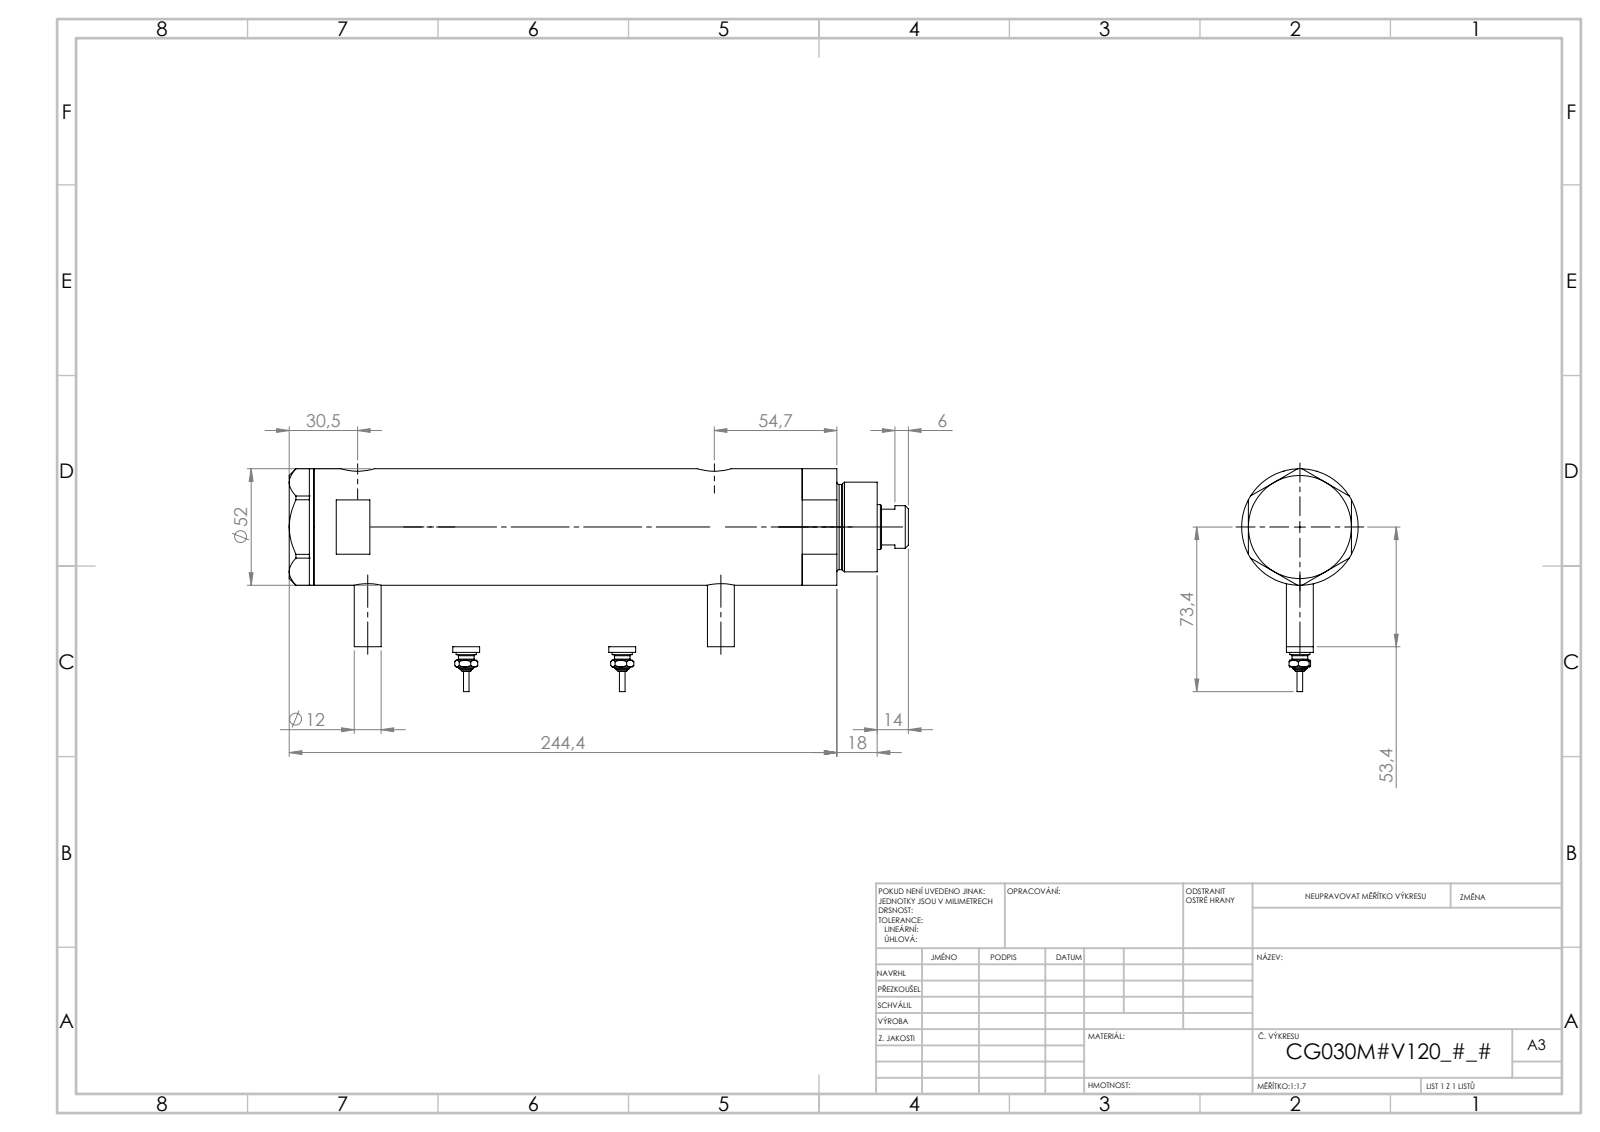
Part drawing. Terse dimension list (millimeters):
name: V270CG_VC; V270CG_BACK; V270CG_MIDDLE; V270CG_SWITCH (+1 more)
written by: SolidWorks 2019 (CONFIG_CONTROL_DESIGN)
unit: mm
bodies: 6 solids, 246 faces (95 planar, 77 cylindrical, 74 other)
size: 269.02 × 84.3 × 52
volume: 478 097 mm³; area: 105 489 mm²
holes: 2× ⌀5, 2× ⌀9.73, 2× ⌀12.5, 2× ⌀15, 1× ⌀6.5, 1× ⌀20, 1× ⌀21.5, 1× ⌀30, 1× ⌀33, 1× ⌀44
bosses: 3× ⌀12, 2× ⌀9, 2× ⌀7, 2× ⌀4.34, 2× ⌀2.4, 1× ⌀52, 1× ⌀40, 1× ⌀38
face distances: 23.8, 11, 34.8, 46, 184.54, 173.54, 149.74, 220.94, 209.94, 186.14
hole spacings: 2.9, 4.5, 146.75, 149.65, 151.25, 154.15, 2.89, 2.91
